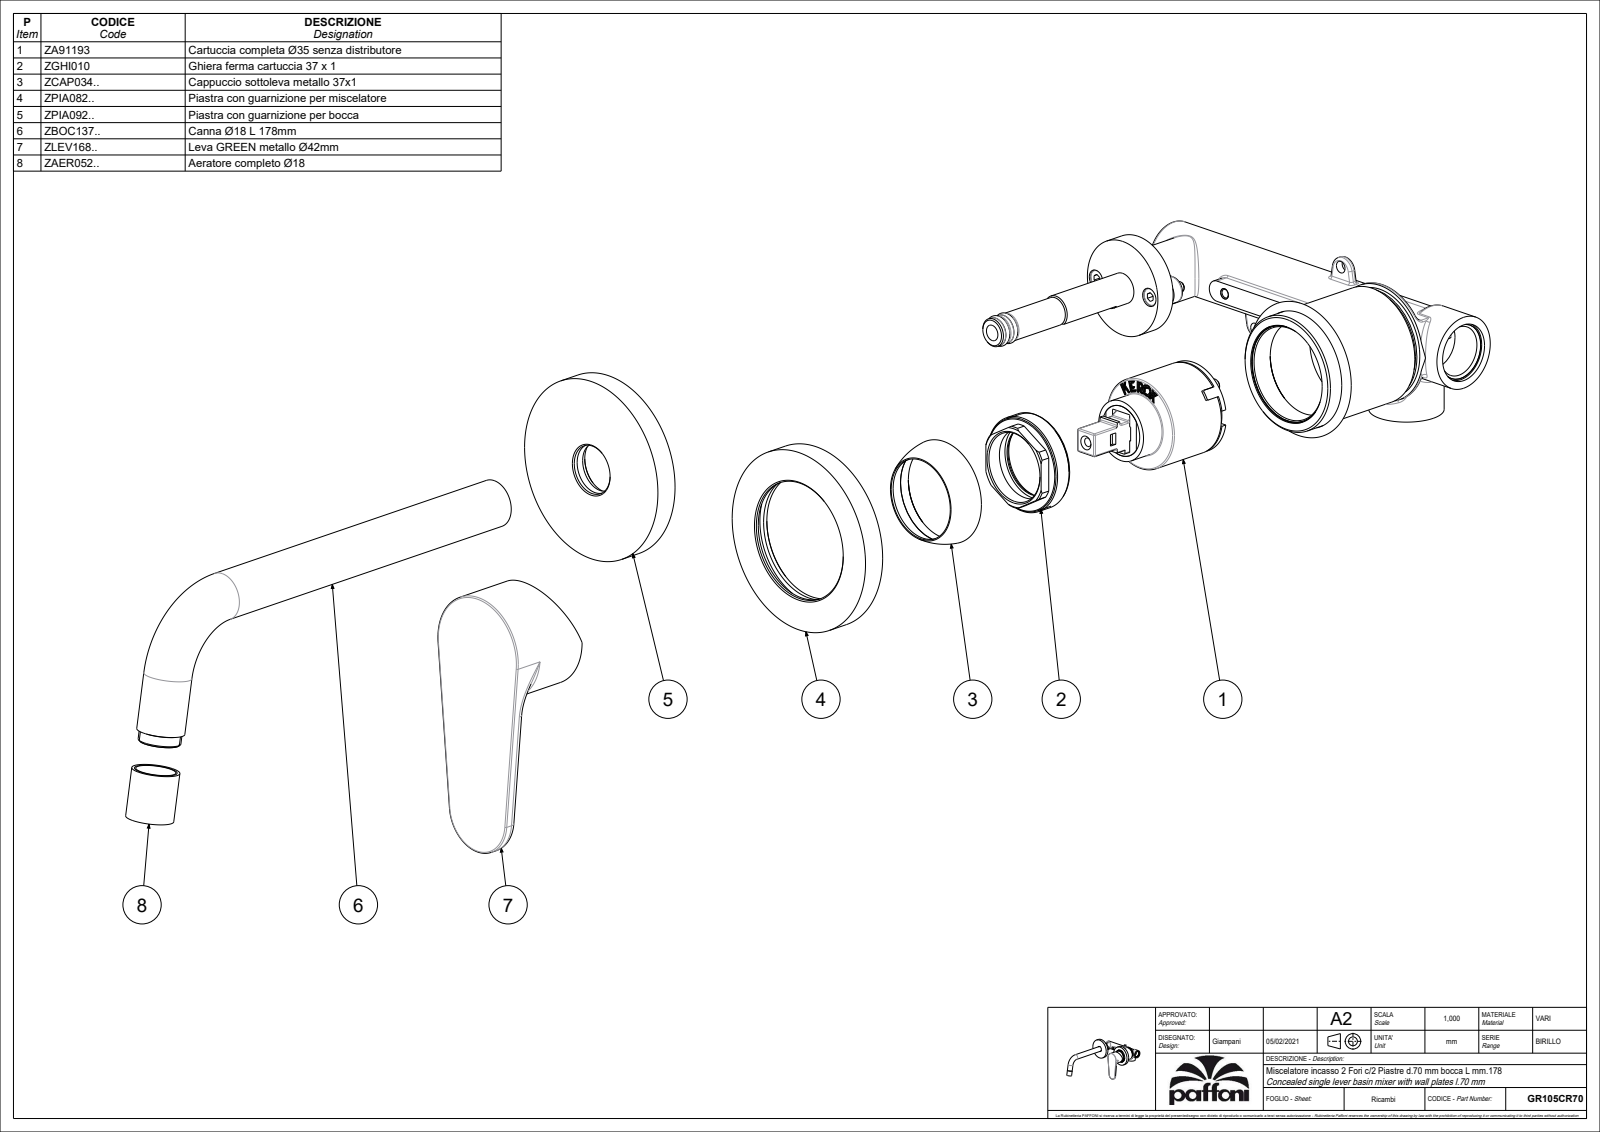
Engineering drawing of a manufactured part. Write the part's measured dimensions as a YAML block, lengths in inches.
part_name: "GR105CR70"
step_written_by: "CREO PARAMETRIC BY PTC INC, 2020044 (CONFIG_CONTROL_DESIGN)"
units: inches
bodies: {solids: 3, faces: 876, planar: 351, cylindrical: 415, other: 110}
overall_size: [7.365, 7.047, 4.506]
volume: 7.114
surface_area: 132.9
round_holes:
  - {diameter: 0.02, count: 51}
  - {diameter: 0.165, count: 2}
  - {diameter: 0.394, count: 2}
  - {diameter: 2.559, count: 2}
  - {diameter: 0.118, count: 1}
  - {diameter: 0.13, count: 1}
  - {diameter: 0.134, count: 1}
  - {diameter: 0.157, count: 1}
  - {diameter: 0.181, count: 1}
  - {diameter: 0.236, count: 1}
  - {diameter: 0.433, count: 1}
  - {diameter: 0.465, count: 1}
round_bosses_or_shafts:
  - {diameter: 2.756, count: 2}
  - {diameter: 0.709, count: 2}
  - {diameter: 0.197, count: 2}
  - {diameter: 2.15, count: 1}
  - {diameter: 1.764, count: 1}
  - {diameter: 1.654, count: 1}
  - {diameter: 1.496, count: 1}
  - {diameter: 1.378, count: 1}
partial_cylinders:
  - {radius: 0.02, count: 26}
  - {radius: 0.012, count: 10}
  - {radius: 0.039, count: 2}
  - {radius: 0.047, count: 2}
  - {radius: 0.118, count: 2}
  - {radius: 0.035, count: 1}
  - {radius: 0.059, count: 1}
  - {radius: 0.112, count: 1}
face_to_face_distances: [0.079, 0.354, 0.276, 2.197, 2.118, 2.472, 0.02, 0.236, 0.098, 0.059]
hole_center_spacings: [0.132, 0.059, 0.083, 0.187, 0.213, 0.118, 0.295, 0.167]
